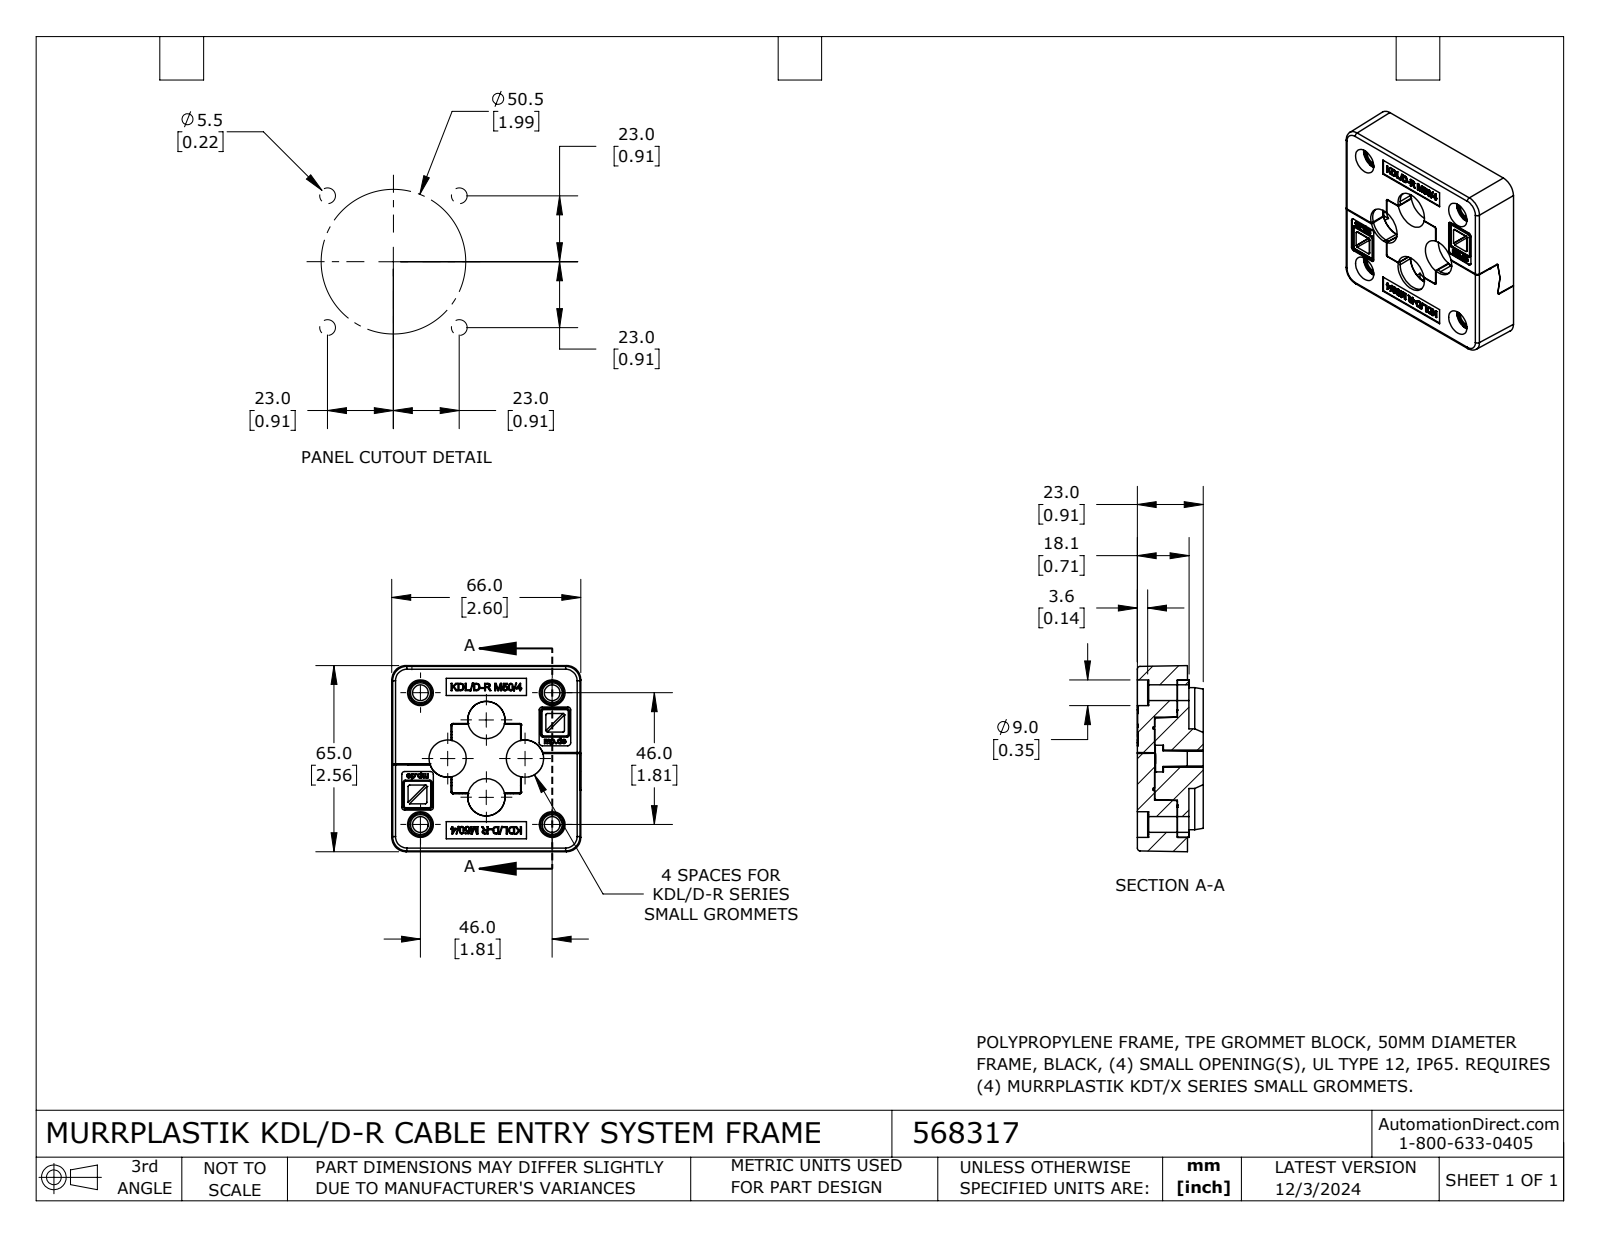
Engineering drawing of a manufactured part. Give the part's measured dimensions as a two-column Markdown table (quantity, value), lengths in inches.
| quantity | value |
| --- | --- |
| part name | 568317 |
| STEP written by | SolidWorks 2024 (AUTOMOTIVE_DESIGN) |
| units | inches |
| bodies | 4 solids, 1627 faces (763 planar, 341 cylindrical, 523 other) |
| overall size | 2.598 × 2.559 × 0.906 |
| volume | 3.773 in³ |
| surface area | 47.26 in² |
| round holes (diameter × count) | 0.197 × 8, 0.217 × 4, 0.276 × 4, 0.354 × 4, 0.589 × 4 |
| round bosses / shafts (diameter × count) | 0.315 × 4 |
| partial cylindrical surfaces (radius × count) | 0.008 × 110, 0.02 × 36, 0.012 × 32, 0.039 × 32, 0.016 × 16, 0.031 × 8, 0.004 × 4, 0.197 × 4 |
| main face-to-face distances | 0.453, 0.236, 0.157, 0.689, 0.217, 0.669, 0.906, 0.551, 2.165, 0.138 |
| hole center spacings | 0.98, 1.698, 0.444, 0.459, 0.543, 0.592, 0.637, 0.752 |
